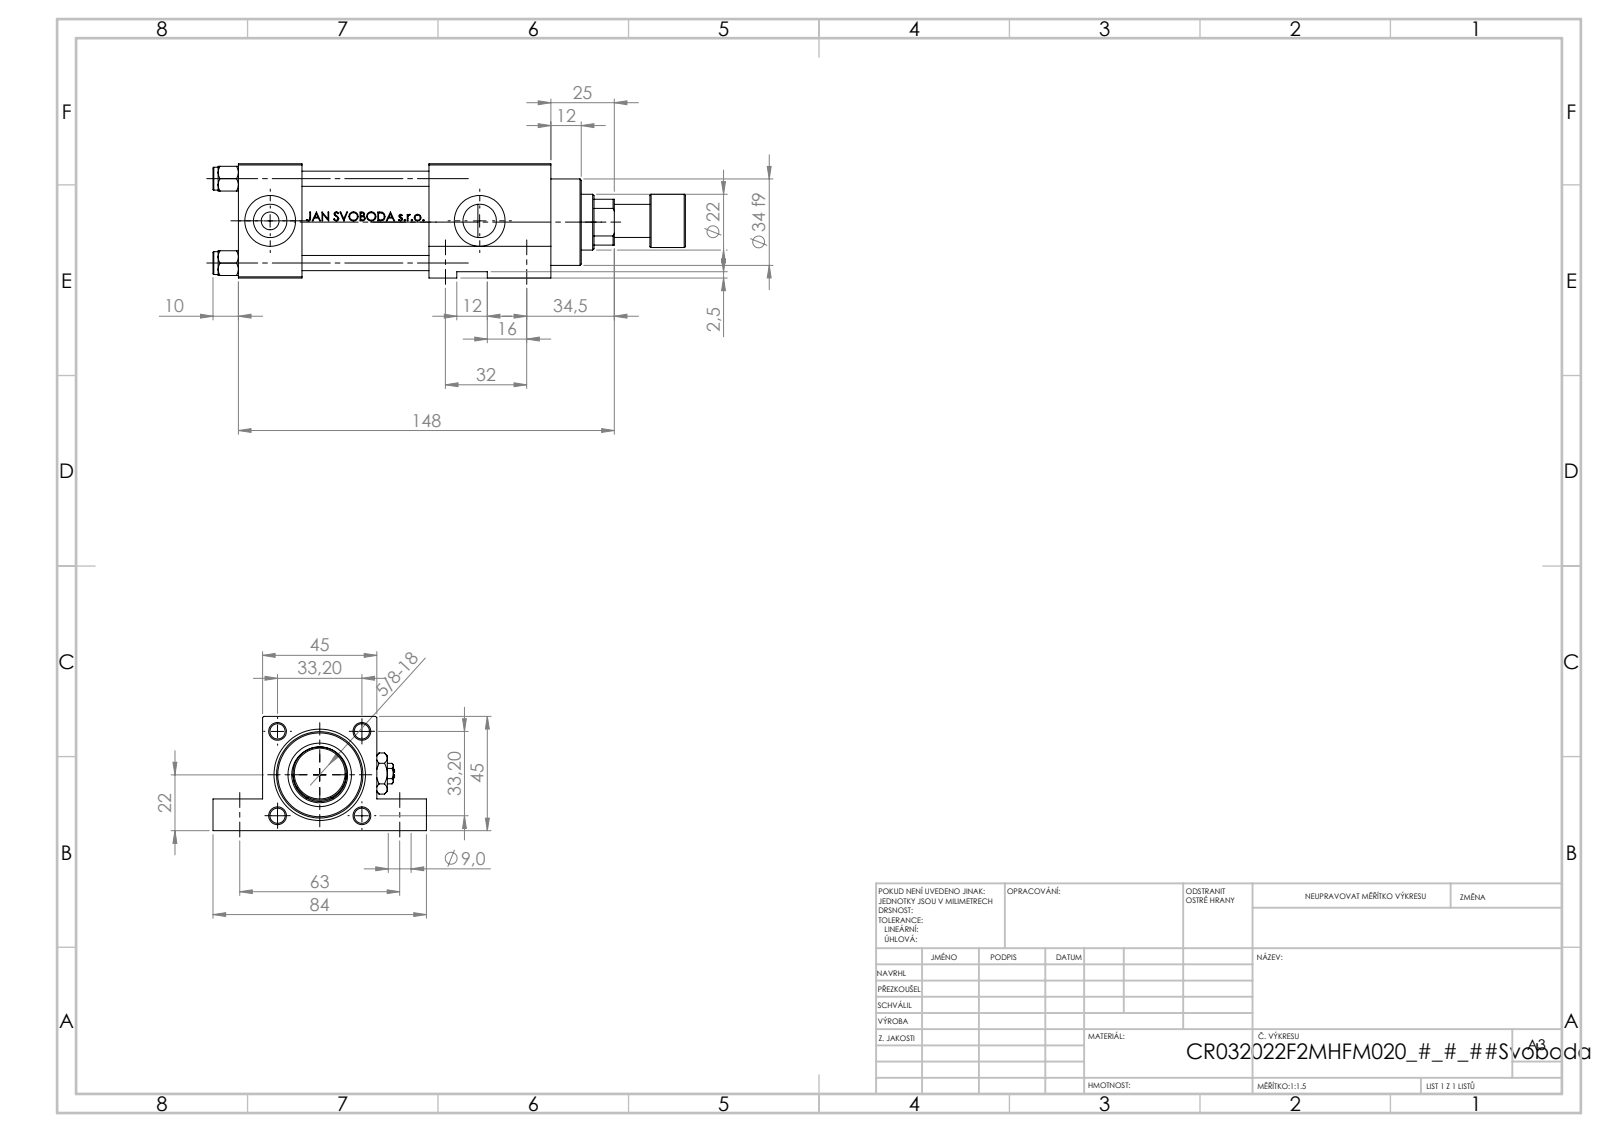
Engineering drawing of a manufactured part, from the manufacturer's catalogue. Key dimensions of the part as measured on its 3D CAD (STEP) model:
Part name (STEP PRODUCT): V215CR_ROD_END_F; Zatka_pro_OIL_PORT; V215CR_F_TYCINKA; NUT_M5_F (+3 more)
STEP written by: SolidWorks 2019 (CONFIG_CONTROL_DESIGN)
Units: millimetres
Bodies: 13 solids, 1161 faces (461 planar, 134 cylindrical, 566 other)
Overall size (bounding box): 186 × 84 × 45
Volume: 233 761 mm³ · Surface area: 80 103 mm²
Round holes (diameter × count): ⌀6 ×4, ⌀9 ×4, ⌀7 ×2, ⌀13.16 ×2, ⌀20 ×2, ⌀10.5 ×1, ⌀13 ×1, ⌀22 ×1, ⌀24 ×1, ⌀25 ×1, ⌀32 ×1, ⌀33 ×1
Round bosses / shafts (diameter × count): ⌀9 ×4, ⌀38 ×1, ⌀34 ×1, ⌀21 ×1, ⌀13 ×1
Partial cylindrical surfaces — rounded edges, fillets, slot ends (radius × count): R10.5 ×1
Main face-to-face distances: 45, 25, 50, 98, 123, 75, 12.5, 32.5, 48, 10
Hole centre spacings: 33.2, 23.13, 23.83, 32, 46.95, 63, 70.66, 82.5
